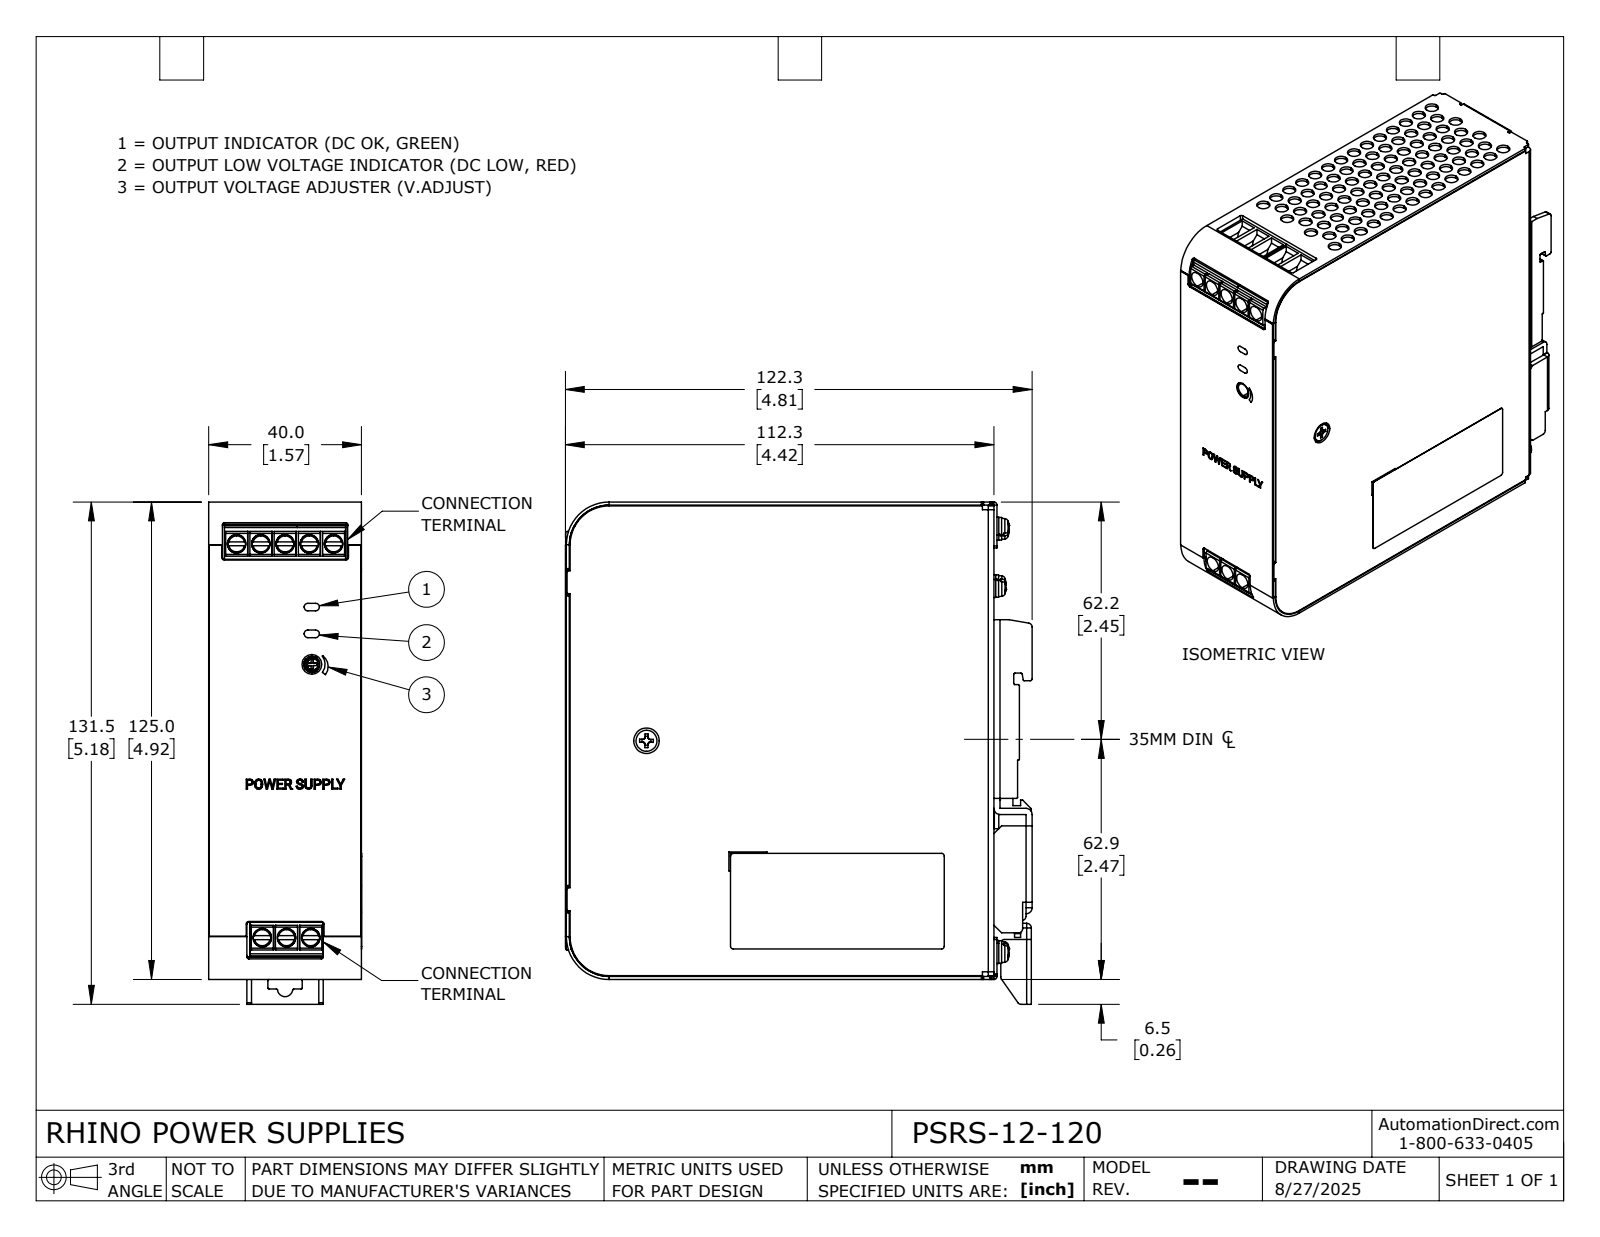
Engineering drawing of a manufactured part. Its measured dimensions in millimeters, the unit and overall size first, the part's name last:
Units: millimetres
Overall size (bounding box): 131.5 × 122.25 × 40.05
Round holes (diameter × count): ⌀4 ×99, ⌀3.6 ×10, ⌀3 ×8, ⌀3.1 ×8, ⌀3.5 ×8, ⌀4.65 ×8, ⌀4.85 ×8, ⌀2.5 ×3, ⌀6.7 ×3, ⌀1.5 ×2, ⌀3.4 ×1, ⌀4.2 ×1
Round bosses / shafts (diameter × count): ⌀3 ×14, ⌀6 ×8, ⌀5.9 ×8, ⌀4.75 ×8, ⌀2.96 ×8, ⌀5.5 ×3
Partial cylindrical surfaces — rounded edges, fillets, slot ends (radius × count): R0.3 ×67, R0.5 ×35, R0.15 ×18, R1 ×14, R1.6 ×13, R0.1 ×9, R1.2 ×9, R0.6 ×2
Main face-to-face distances: 40, 0.8, 112.25, 1.6, 124.2, 125, 10, 8.4, 2, 1.2
Hole centre spacings: 5.6, 11.72, 11.2, 10.3, 16.8, 15.22, 47.88, 53.45
Volume: 559 901 mm³ · Surface area: 72 533 mm²
Bodies: 2 solids, 2380 faces (1209 planar, 866 cylindrical, 305 other)
Part name (STEP PRODUCT): PSRS-12-120
STEP written by: SolidWorks 2024 (AUTOMOTIVE_DESIGN)
